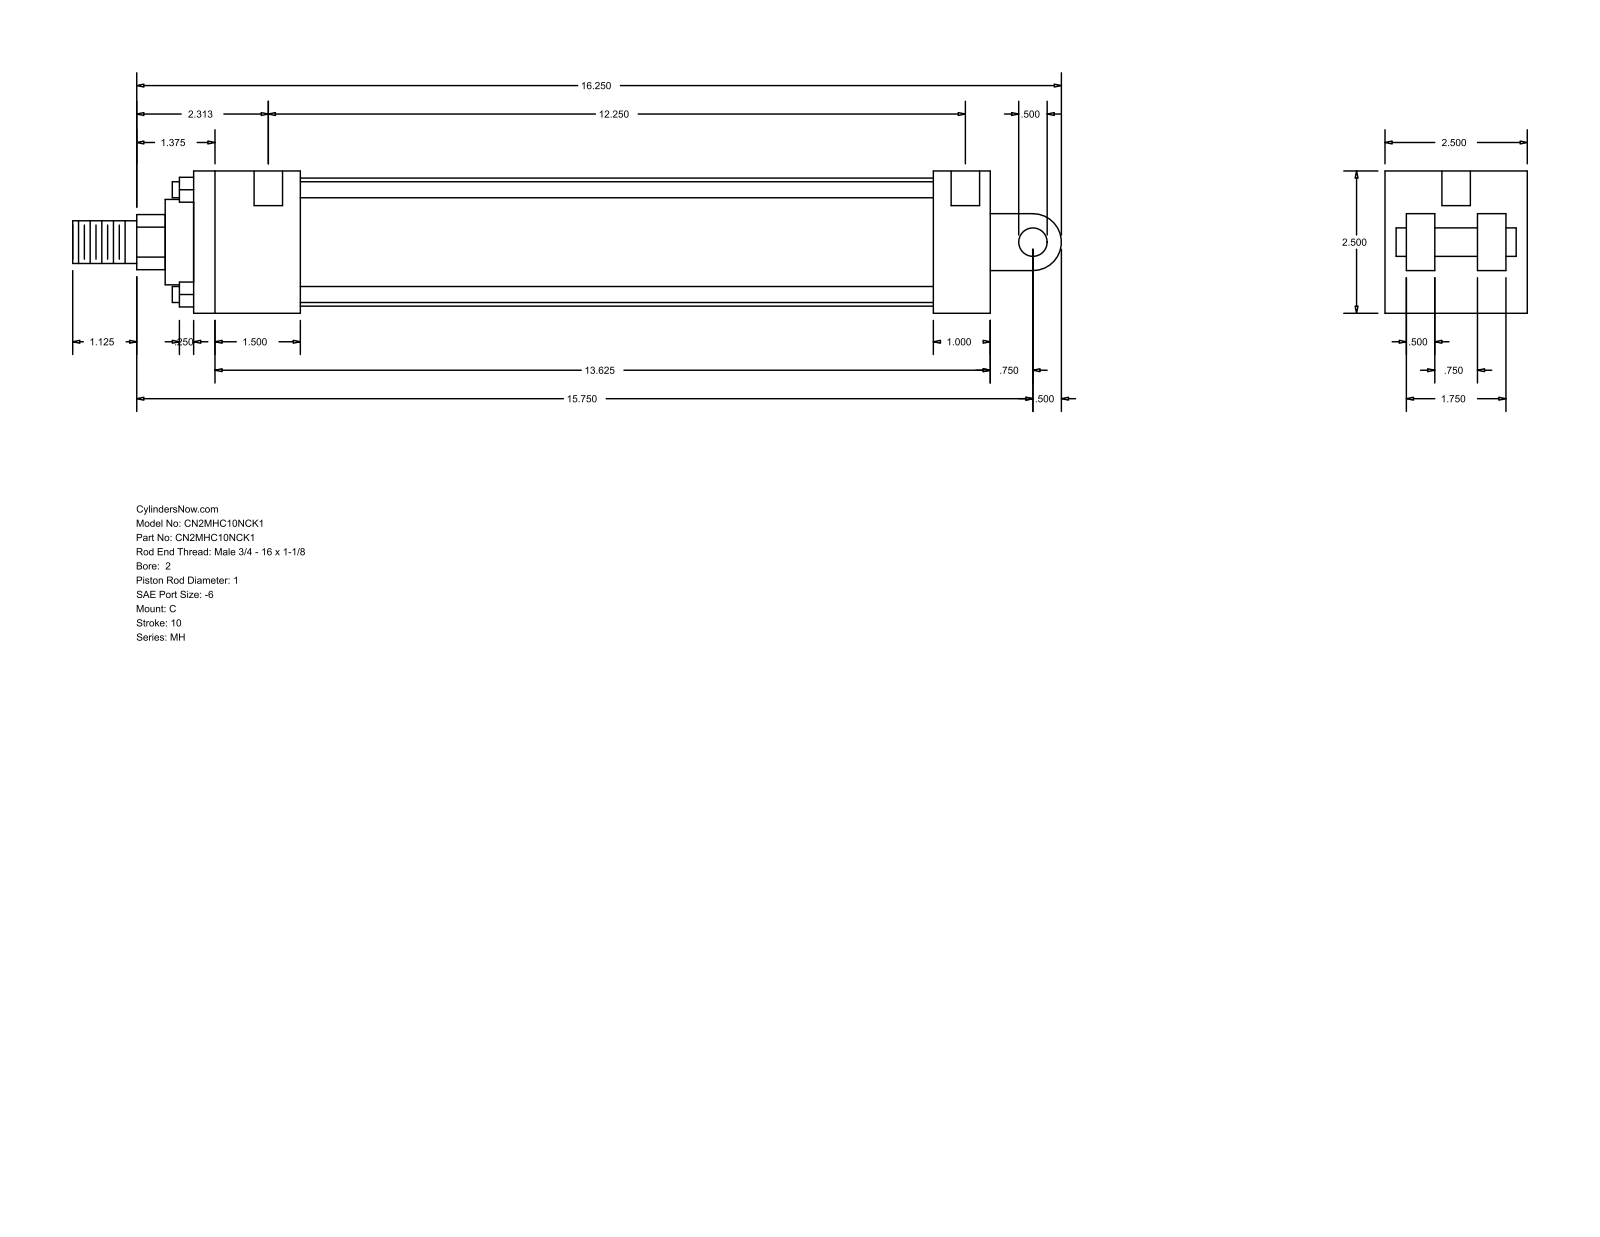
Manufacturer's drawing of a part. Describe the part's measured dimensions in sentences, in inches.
The part is named "MH_C__0200_1". Its 3-D file was written by "GSSL Pune (CONFIG_CONTROL_DESIGN)". It is 0 solids with 99 faces: 70 planar, 29 cylindrical and 0 other. Overall it measures 17.375 by 2.5 by 2.5 inches. Round holes: 4 of diameter 0.219, 2 of diameter 0.5. Round bosses or shafts: 4 of diameter 0.281, 1 of diameter 2.25, 1 of diameter 1.5, 1 of diameter 1, 1 of diameter 0.75, 1 of diameter 0.5. Partial cylindrical surfaces (rounded edges, fillets, slot ends): 1 of radius 0.484, 1 of radius 0.5. The main face-to-face distances are 2.5, 14, 0.5, 1, 1.875, 2.125, 0.375, 13, 11.125, 12.125. The hole center spacings are 12.562, 0.125, 0.187, 12.25, 12.375, 12.437.
